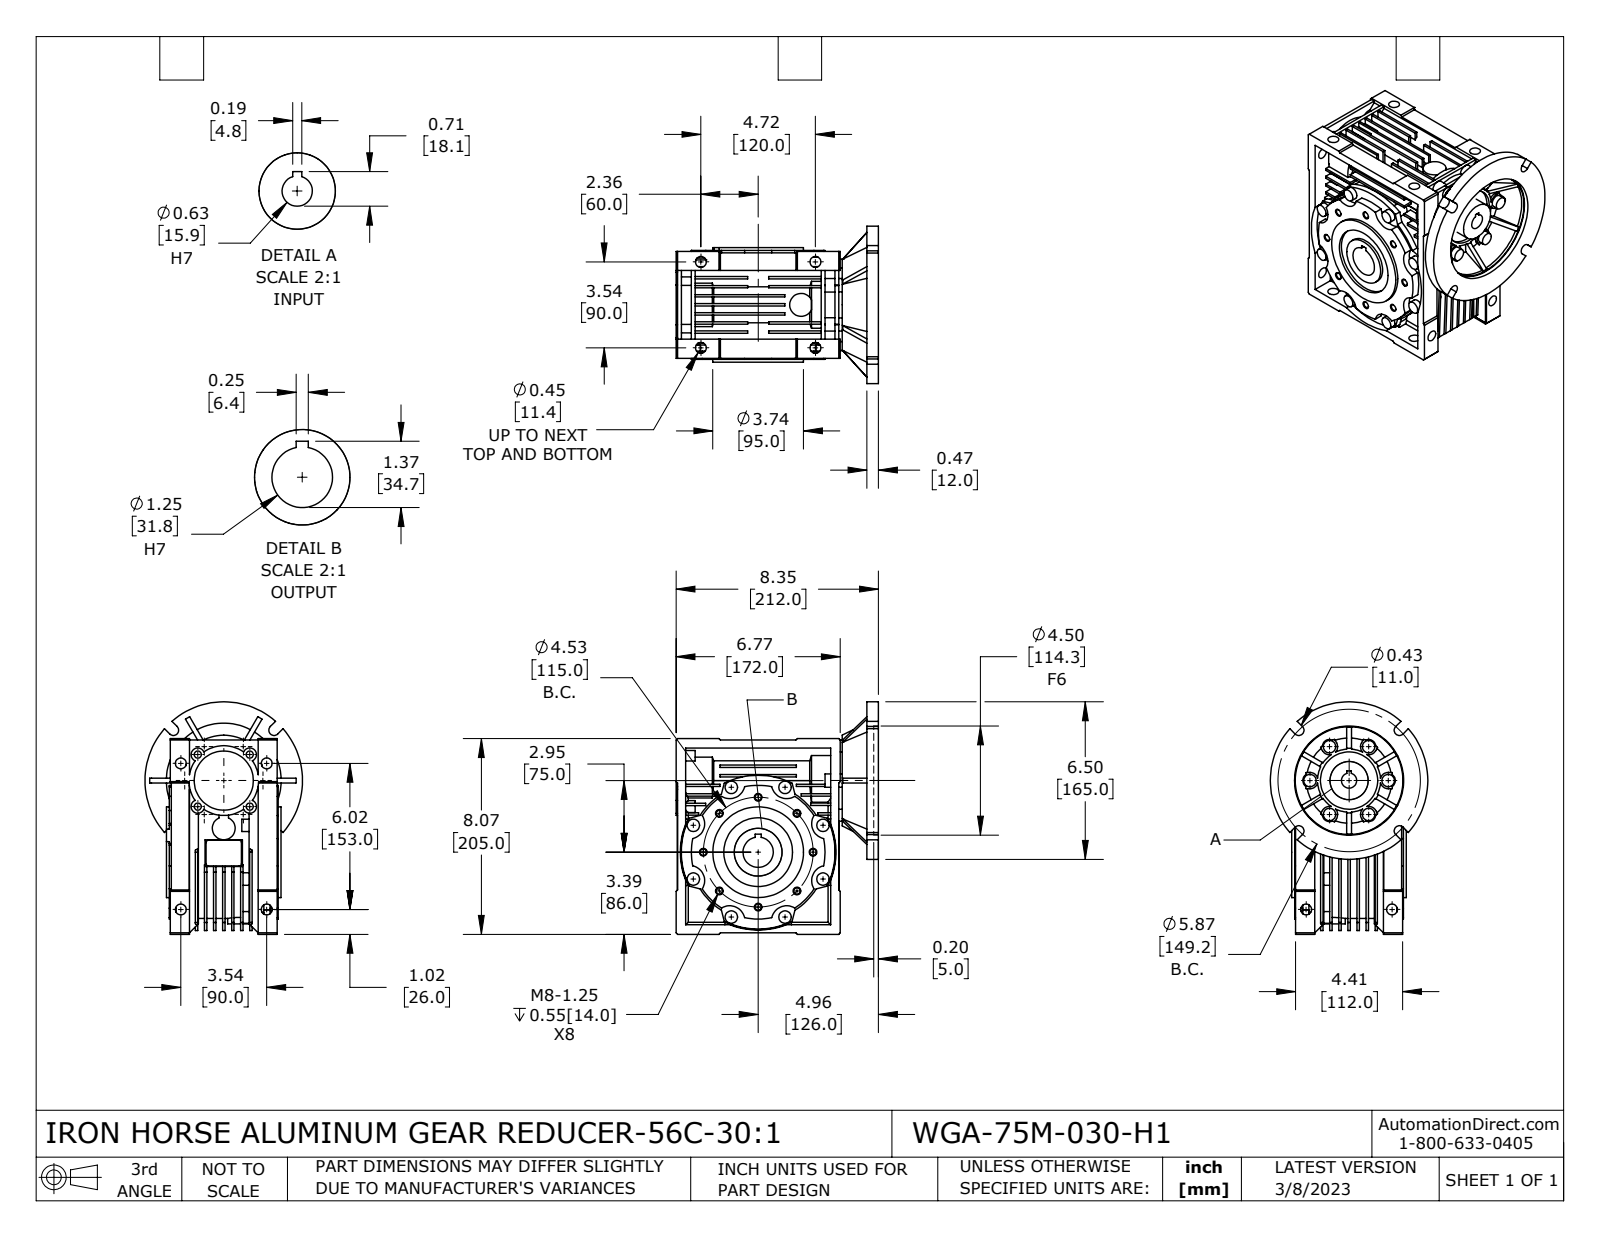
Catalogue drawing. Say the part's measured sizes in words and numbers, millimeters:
The part is named "WGA-75M-030-H1". Its 3-D file was written by "SolidWorks 2021 (CONFIG_CONTROL_DESIGN)". It is 4 solids with 1179 faces: 675 planar, 386 cylindrical and 118 other. Overall it measures 243.5 by 212 by 165 millimeters. Its volume is 2 963 000 cubic millimeters and its surface area 503 000 square millimeters. Round holes: 8 of diameter 6.7, 8 of diameter 11.4, 4 of diameter 7.4, 1 of diameter 15.9, 1 of diameter 16.5, 1 of diameter 25.4, 1 of diameter 31.8, 1 of diameter 39, 1 of diameter 42, 1 of diameter 50, 1 of diameter 62, 1 of diameter 68. Round bosses or shafts: 14 of diameter 13, 3 of diameter 24, 1 of diameter 165, 1 of diameter 139.9, 1 of diameter 138.8, 1 of diameter 95, 1 of diameter 76, 1 of diameter 71. Partial cylindrical surfaces (rounded edges, fillets, slot ends): 10 of radius 7, 8 of radius 16, 6 of radius 7.5, 6 of radius 8.5, 4 of radius 2.5, 4 of radius 5.5, 1 of radius 33, 1 of radius 36. The main face-to-face distances are 9.5, 2.5, 12, 19, 7, 28.5, 38, 10, 16.5, 21.5. The hole center spacings are 57.5, 44, 81.3, 106.2, 38.5, 54.4, 90, 115.
